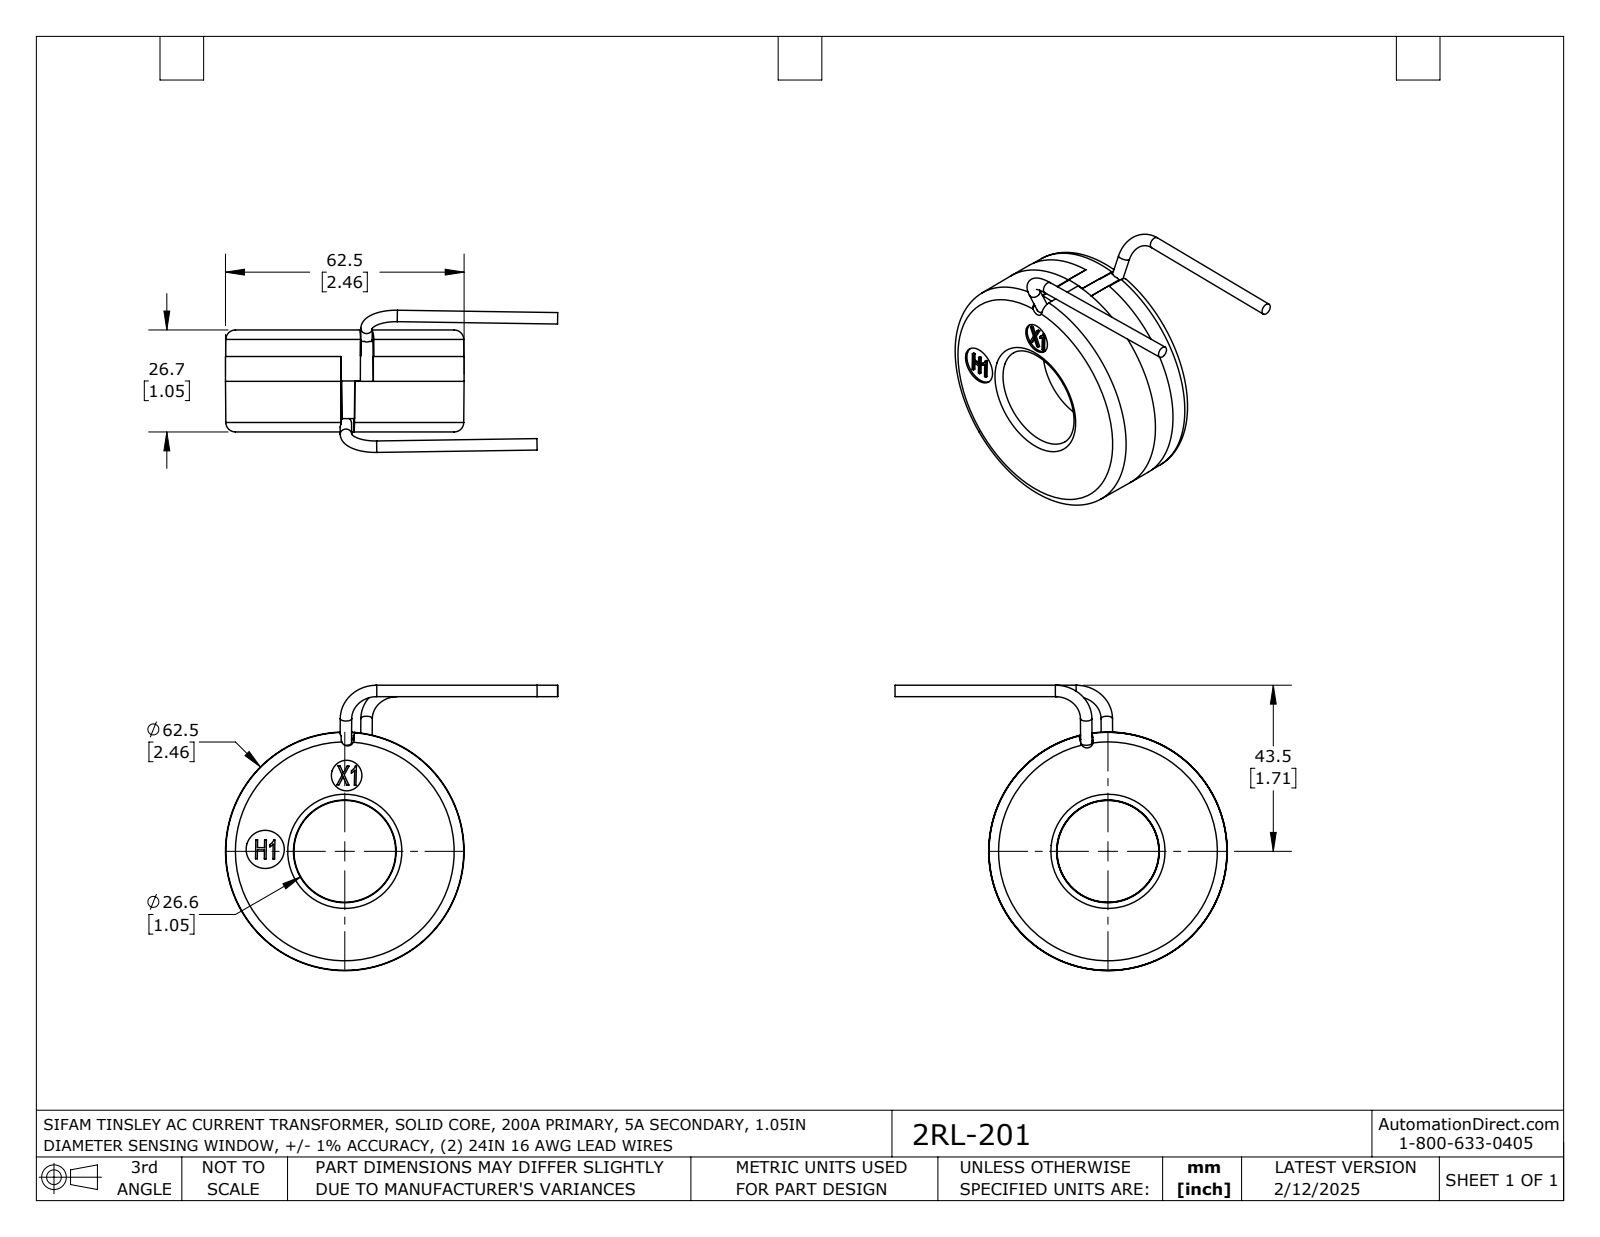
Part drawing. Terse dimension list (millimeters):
name: 2RL-201
written by: SolidWorks 2021 (AUTOMOTIVE_DESIGN)
unit: mm
bodies: 1 solid, 129 faces (62 planar, 18 cylindrical, 49 other)
size: 87.4 × 74.8 × 37.2
volume: 66 680 mm³; area: 13 430 mm²
holes: 1× ⌀8, 1× ⌀10, 1× ⌀60.5
bosses: 4× ⌀3, 1× ⌀62.5
face distances: 26.7, 0.5, 26.2, 0.5, 26.2, 19.8, 19.3, 19.3, 7, 13.4
hole spacings: 19.9, 20.9, 28.8
